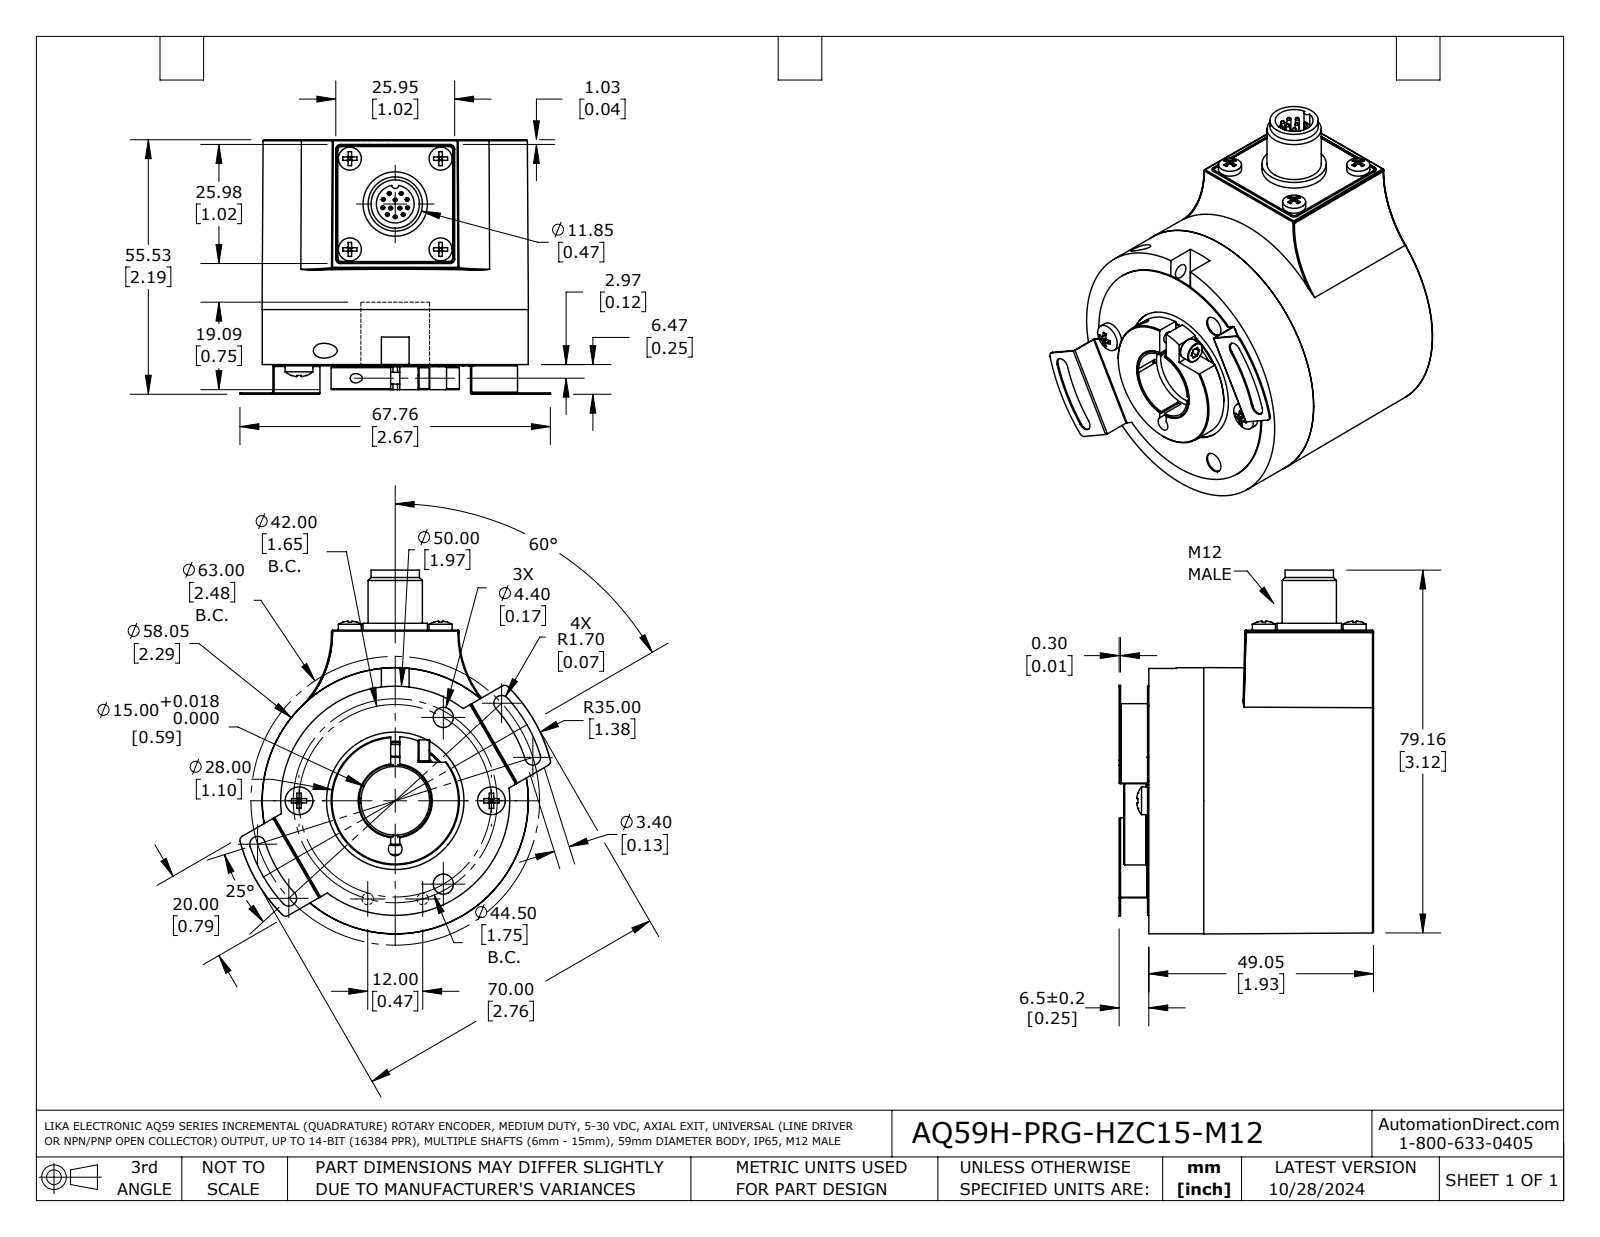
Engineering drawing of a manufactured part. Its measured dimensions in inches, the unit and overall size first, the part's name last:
Units: inches
Overall size (bounding box): 3.126 × 2.669 × 2.186
Round holes (diameter × count): ⌀0.03 ×12, ⌀0.098 ×4, ⌀0.195 ×4, ⌀0.173 ×2, ⌀0.081 ×1, ⌀0.096 ×1, ⌀0.128 ×1, ⌀0.161 ×1, ⌀0.175 ×1, ⌀0.325 ×1, ⌀0.411 ×1, ⌀0.463 ×1
Round bosses / shafts (diameter × count): ⌀0.033 ×12, ⌀0.199 ×4, ⌀0.238 ×2, ⌀2.285 ×1, ⌀1.102 ×1, ⌀0.77 ×1, ⌀0.748 ×1, ⌀0.624 ×1
Partial cylindrical surfaces — rounded edges, fillets, slot ends (radius × count): R0.009 ×39, R0.007 ×23, R0.006 ×9, R0.008 ×9, R0.008 ×8, R0.005 ×6, R0.006 ×4, R0.012 ×4
Main face-to-face distances: 1.93, 1.931, 1.88, 1.879, 0.051, 1.942, 1.941, 0.062, 2.146, 1.95
Hole centre spacings: 0.827, 0.551, 0.604, 0.78, 0.071, 0.102, 0.146, 0.053
Volume: 0.281 in³ · Surface area: 67.22 in²
Bodies: 8 solids, 1089 faces (505 planar, 305 cylindrical, 279 other)
Part name (STEP PRODUCT): AQ59H-PRG-HZC15-M12
STEP written by: SolidWorks 2021 (AUTOMOTIVE_DESIGN)
